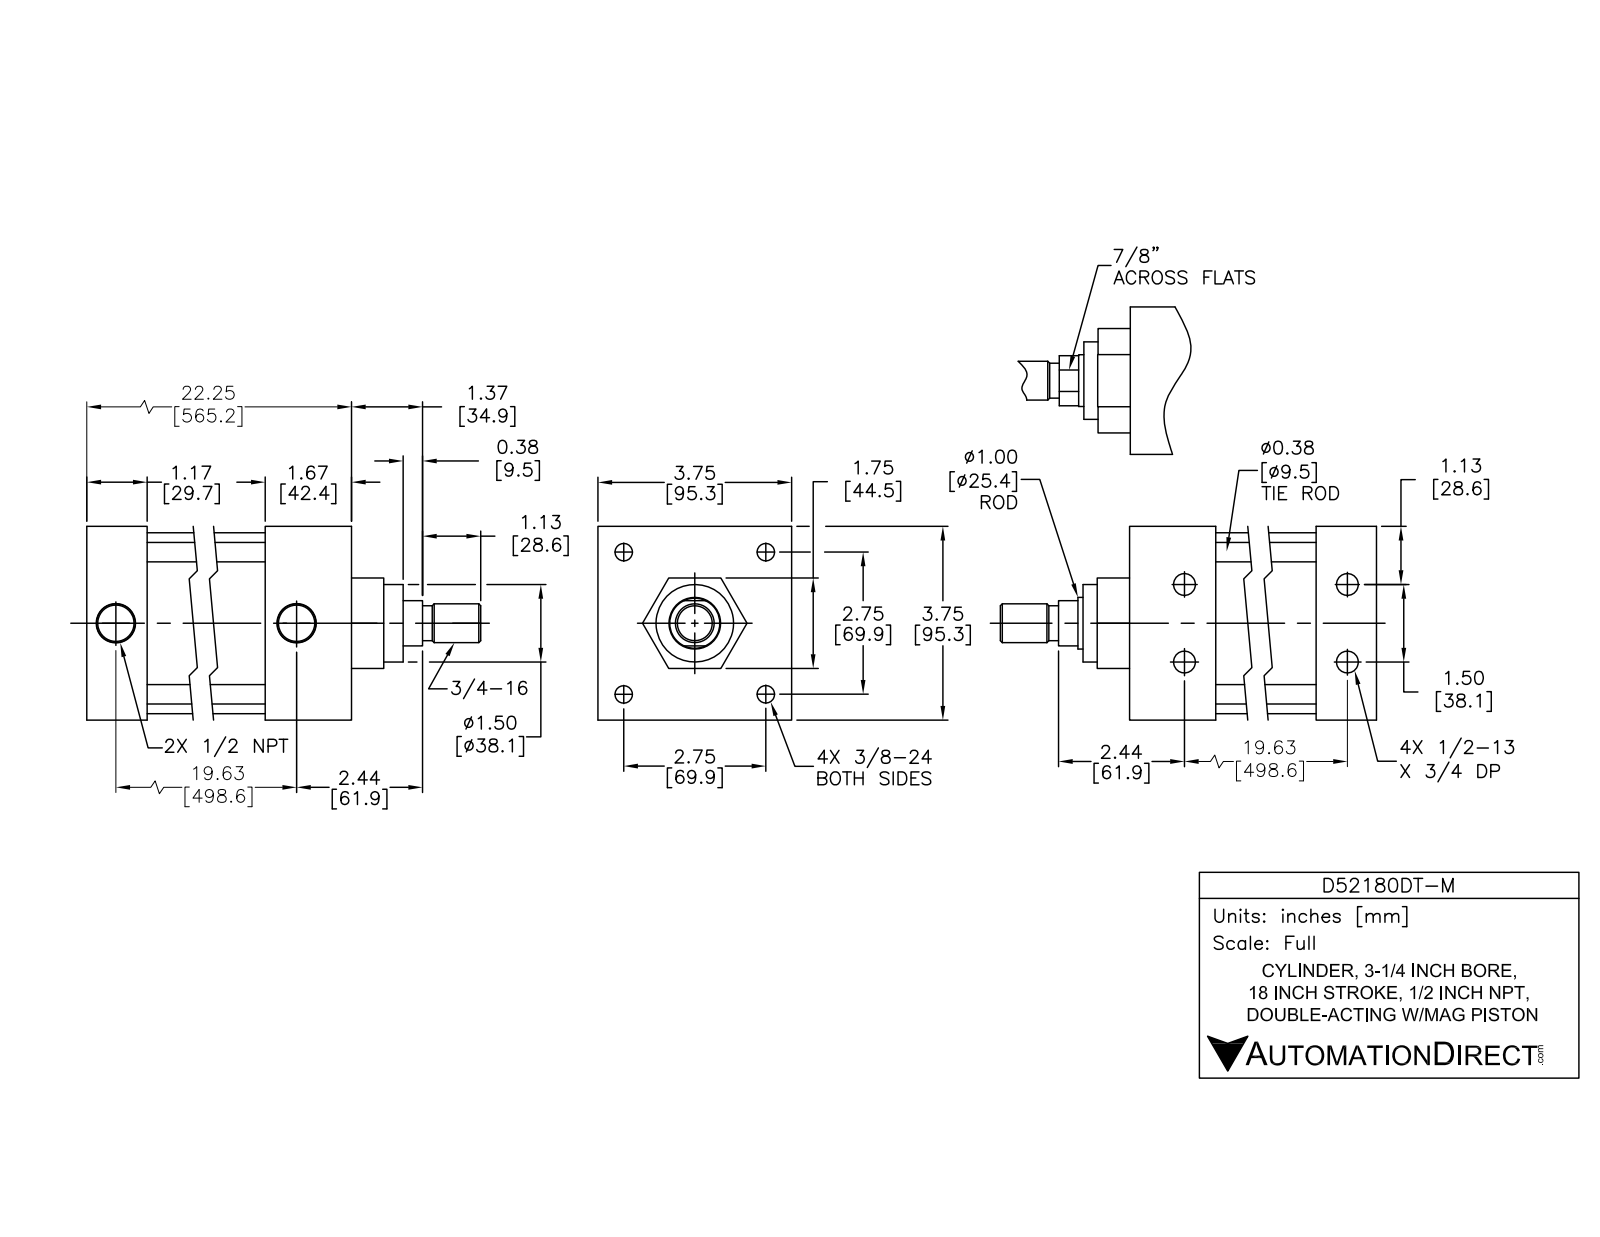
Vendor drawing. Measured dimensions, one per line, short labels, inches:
name: D52180DT-M; D52180DT-M BODY; D52180DT-M PISTON
written by: SolidWorks 2015 (AUTOMOTIVE_DESIGN)
unit: in
bodies: 12 solids, 303 faces (99 planar, 114 cylindrical, 90 other)
size: 24.745 × 3.75 × 3.75
volume: 98.27 in³; area: 752.1 in²
holes: 4× ⌀0.33, 4× ⌀0.406, 4× ⌀0.417, 4× ⌀0.625, 2× ⌀0.5, 2× ⌀0.766, 1× ⌀1, 1× ⌀1.003, 1× ⌀3.25
bosses: 4× ⌀0.609, 4× ⌀0.375, 4× ⌀0.34, 1× ⌀3.5, 1× ⌀3.247, 1× ⌀1.75, 1× ⌀0.997, 1× ⌀0.97
rounds: 4× R0.375
face distances: 3.75, 0.08, 19.326, 22.246, 1.75, 20.997, 1.249, 19.751, 1.246, 2.495
hole spacings: 2.758, 1.95, 0.75, 0.76, 1.5, 3.9, 20.5, 20.518
